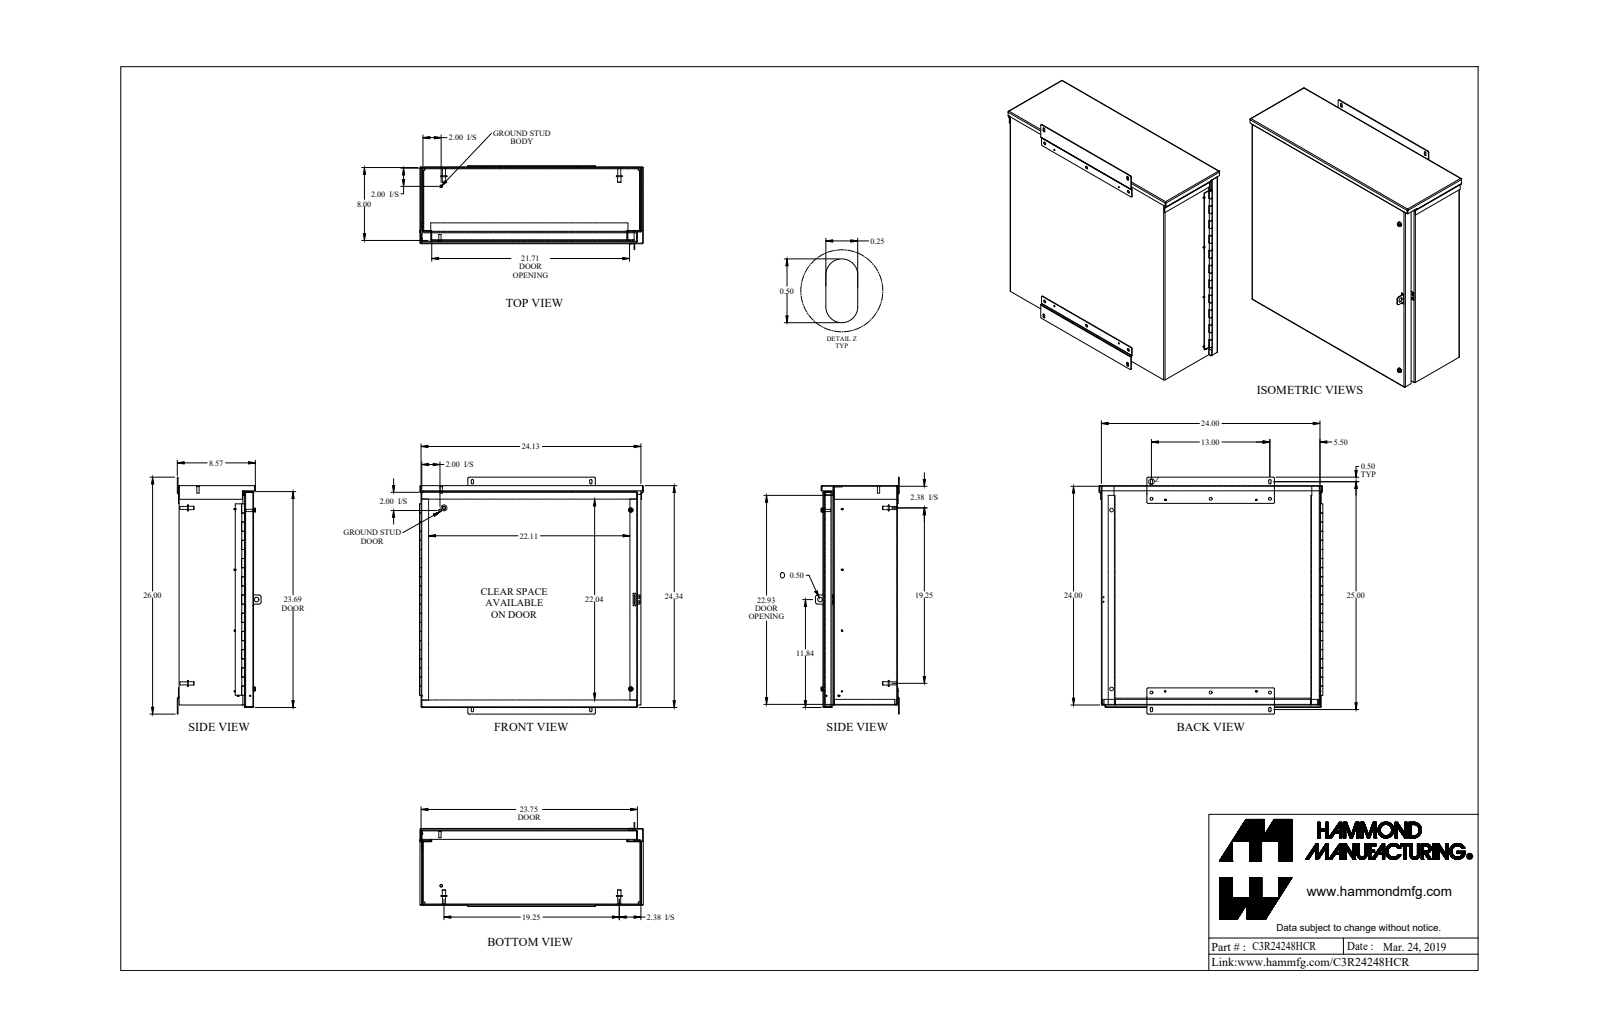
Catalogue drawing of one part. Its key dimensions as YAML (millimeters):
part_name: "C3R24248HCR_Default"
step_written_by: "SolidWorks 2019 (CONFIG_CONTROL_DESIGN)"
units: millimeters
bodies: {solids: 33, faces: 888, planar: 499, cylindrical: 335, other: 54}
overall_size: [660.4, 624.1, 233.6]
volume: 2974000
surface_area: 3165000
round_holes:
  - {diameter: 8, count: 9}
  - {diameter: 3.5, count: 4}
  - {diameter: 3.6, count: 4}
  - {diameter: 6.6, count: 3}
  - {diameter: 6.8, count: 2}
  - {diameter: 7.1, count: 2}
  - {diameter: 7.4, count: 2}
  - {diameter: 10.1, count: 2}
  - {diameter: 4.8, count: 1}
  - {diameter: 12.7, count: 1}
round_bosses_or_shafts:
  - {diameter: 3.3, count: 10}
  - {diameter: 16.5, count: 4}
  - {diameter: 9.5, count: 4}
  - {diameter: 8.4, count: 4}
  - {diameter: 13, count: 3}
  - {diameter: 6.2, count: 3}
  - {diameter: 4.7, count: 3}
  - {diameter: 12.7, count: 2}
partial_cylinders:
  - {radius: 0.9, count: 31}
  - {radius: 2.7, count: 31}
  - {radius: 3.2, count: 19}
  - {radius: 4.3, count: 3}
  - {radius: 6.4, count: 2}
face_to_face_distances: [1.8, 205.7, 203.9, 207.6, 609.6, 607.8, 611.4, 605.9, 23.6, 25.4]
hole_center_spacings: [38.2, 127.1, 165.1, 292.1, 537.9, 551.4, 564.4, 610.9]
